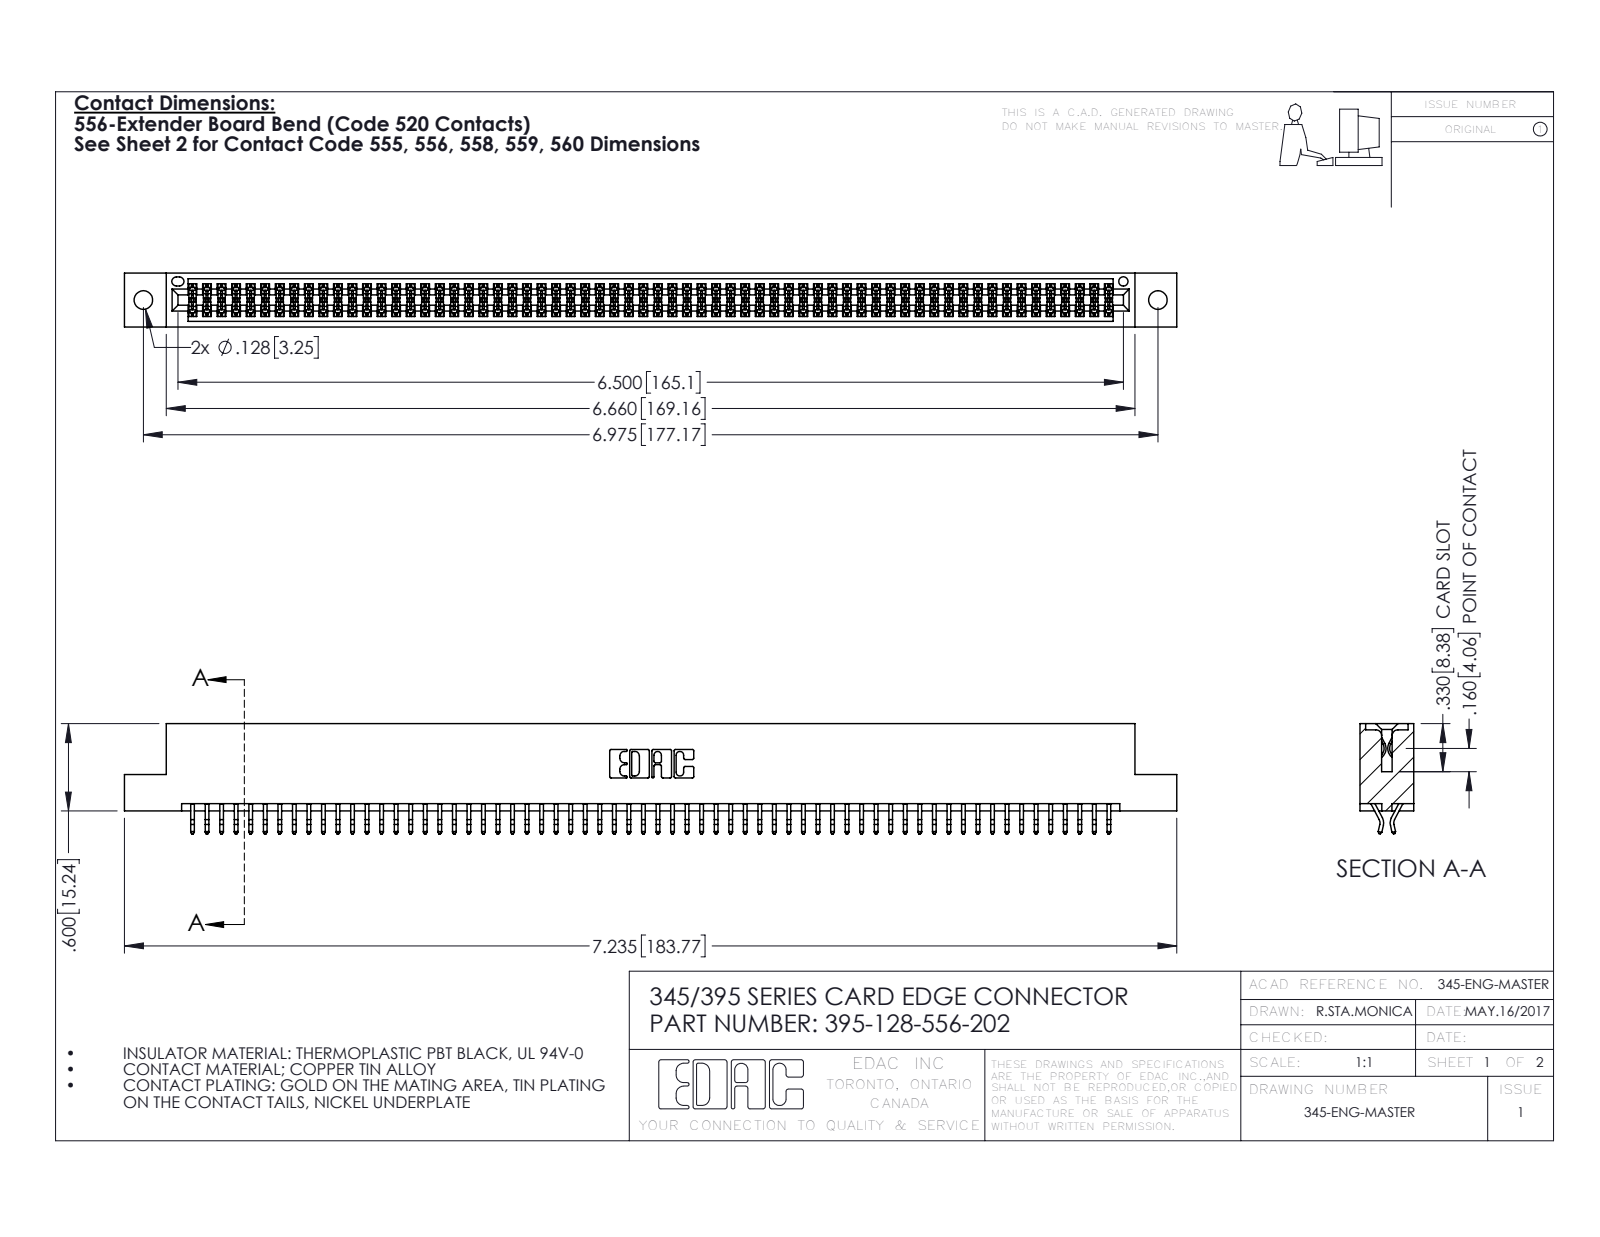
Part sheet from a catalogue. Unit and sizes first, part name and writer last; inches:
Units: inches
Overall size (bounding box): 7.235 × 0.757 × 0.37
Round holes (diameter × count): ⌀0.128 ×2, ⌀0.064 ×1
Partial cylindrical surfaces — rounded edges, fillets, slot ends (radius × count): R0.006 ×192, R0.01 ×22, R0.007 ×6, R0.031 ×6, R0.026 ×3, R0.01 ×2, R0.014 ×2, R0.019 ×2
Main face-to-face distances: 0.298, 0.072, 0.37, 0.2, 0.025, 0.098, 0.272, 0.225, 0.175, 0.149
Hole centre spacings: 0.27, 6.739, 6.975
Volume: 1.099 in³ · Surface area: 41.34 in²
Bodies: 129 solids, 7294 faces (4816 planar, 2478 cylindrical, 0 other)
Part name (STEP PRODUCT): 395-128-556-202; 345-292-001_556 Tail; 345 Part_Flush Mounting Lugs - 0.128 Dia
STEP written by: SolidWorks 2016 (CONFIG_CONTROL_DESIGN)
